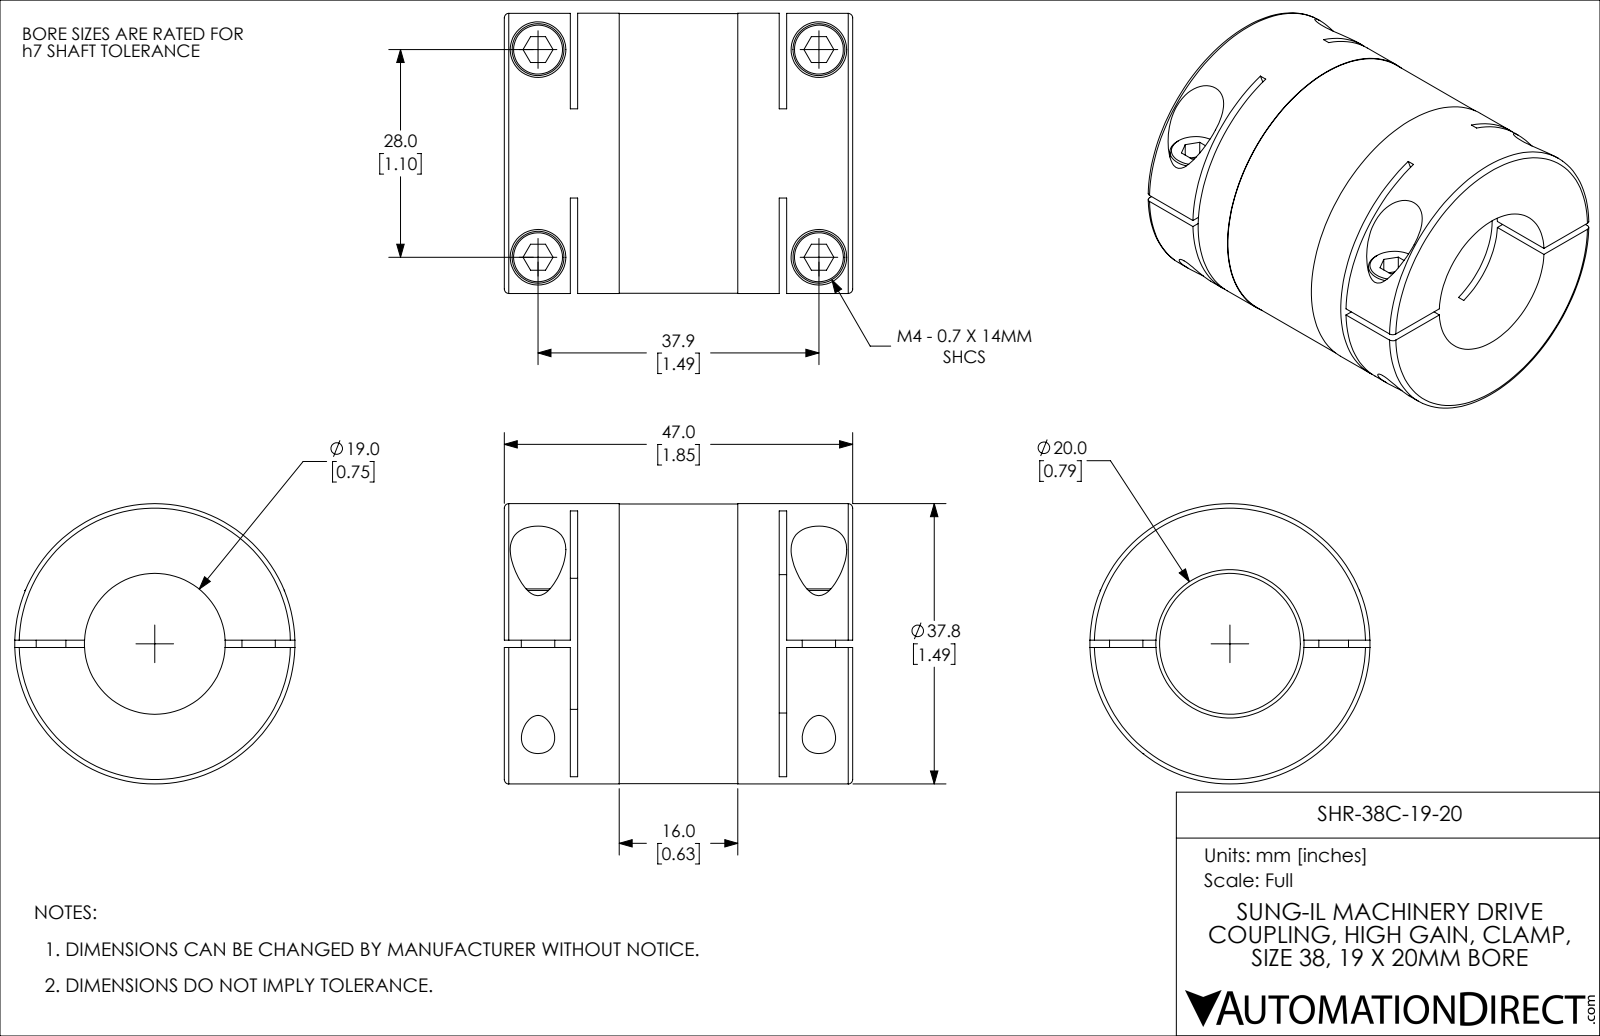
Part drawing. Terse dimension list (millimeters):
name: SHR-38C-19-20
written by: SolidWorks 2021 (CONFIG_CONTROL_DESIGN)
unit: mm
bodies: 1 solid, 144 faces (70 planar, 58 cylindrical, 16 other)
size: 47 × 37.8 × 37.8
volume: 34 372 mm³; area: 15 098 mm²
holes: 4× ⌀4.5, 4× ⌀7.5, 1× ⌀19, 1× ⌀20, 1× ⌀22
bosses: 4× ⌀7, 2× ⌀4, 1× ⌀37.8, 1× ⌀37.7
rounds: 2× R50
face distances: 1, 9.9, 37.1, 8.9, 38.1, 28.2, 47, 27.2, 29.2, 31.5
hole spacings: 28, 37.9, 47.12
